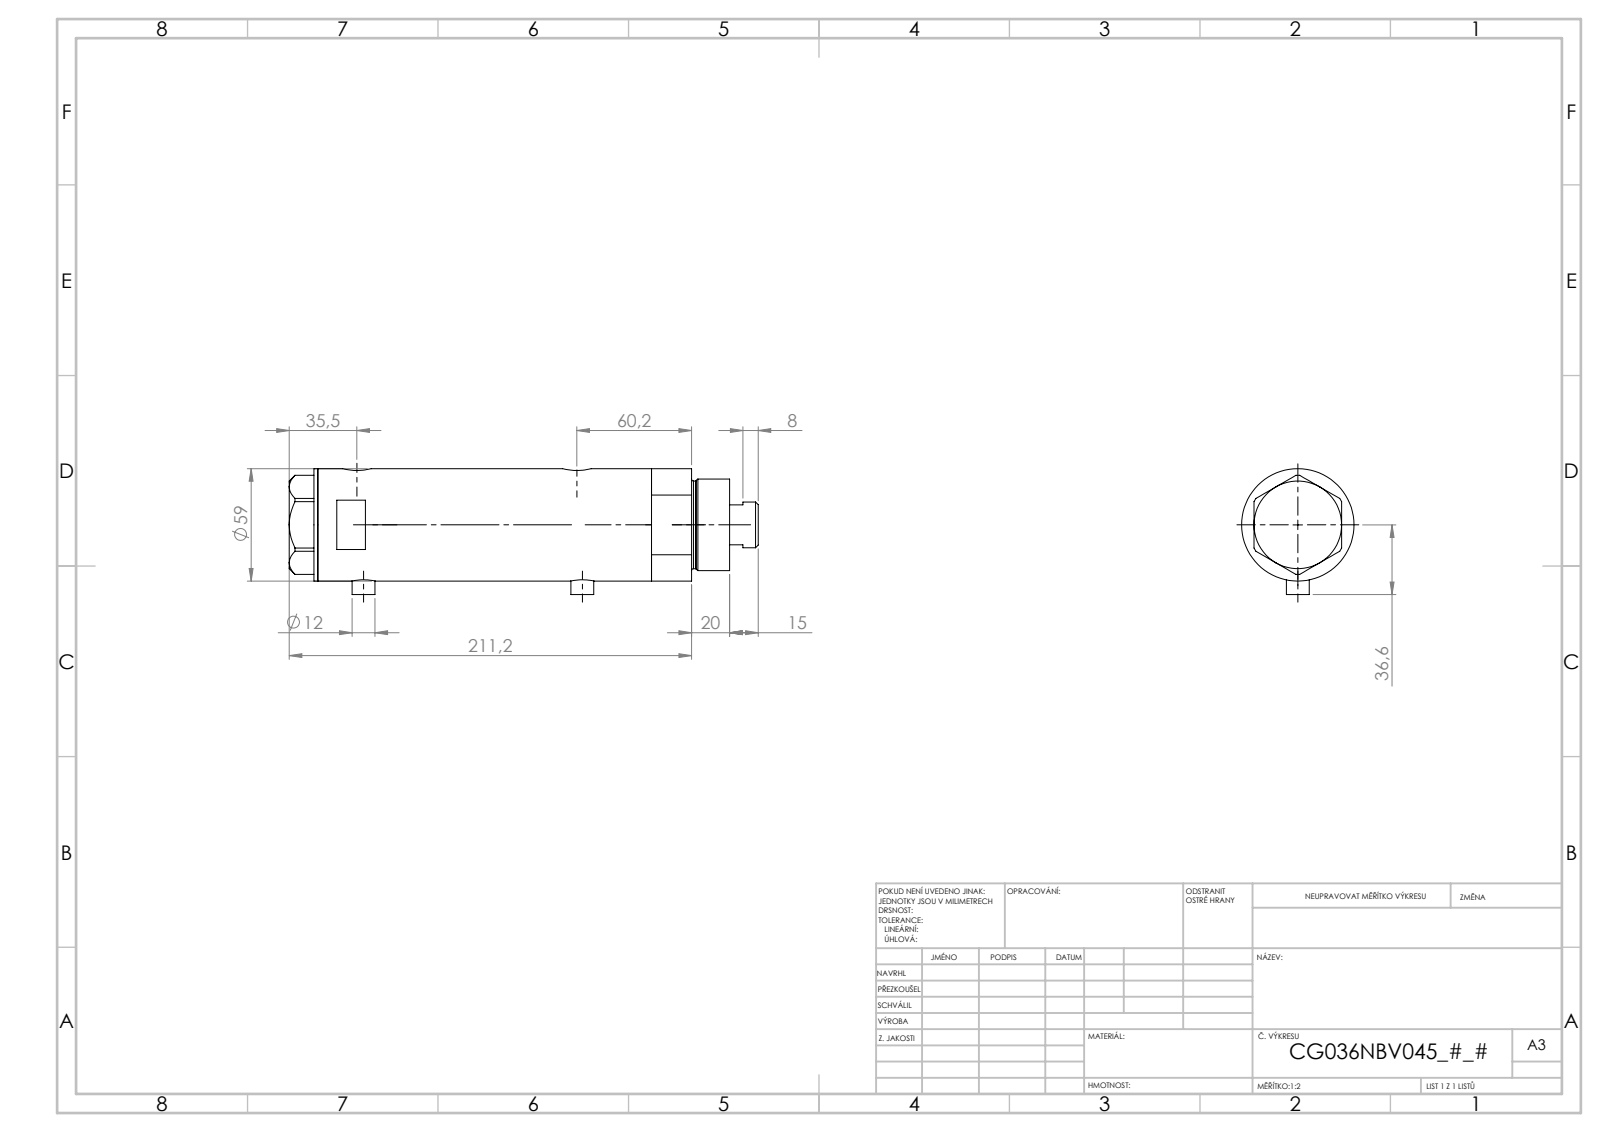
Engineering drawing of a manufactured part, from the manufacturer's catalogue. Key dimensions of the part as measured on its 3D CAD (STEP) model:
Part name (STEP PRODUCT): V270CG_MIDDLE; V270CG_BACK; V270CG_VC; V270CG_FRONT
STEP written by: SolidWorks 2019 (CONFIG_CONTROL_DESIGN)
Units: millimetres
Bodies: 4 solids, 120 faces (51 planar, 49 cylindrical, 20 other)
Overall size (bounding box): 246.2 × 66.1 × 59
Volume: 576 768 mm³ · Surface area: 114 552 mm²
Round holes (diameter × count): ⌀9.73 ×2, ⌀12.5 ×2, ⌀15 ×2, ⌀8.5 ×1, ⌀25 ×1, ⌀26.5 ×1, ⌀36 ×1, ⌀40 ×1, ⌀52 ×1
Round bosses / shafts (diameter × count): ⌀12 ×2, ⌀59 ×1, ⌀48 ×1, ⌀46 ×1, ⌀24 ×1
Main face-to-face distances: 137.2, 23.5, 113.7, 15, 38.5, 152.2, 2, 231.2, 216.2, 192.7
Hole centre spacings: 2.9, 3.5, 112, 114.9, 115.5, 118.4
